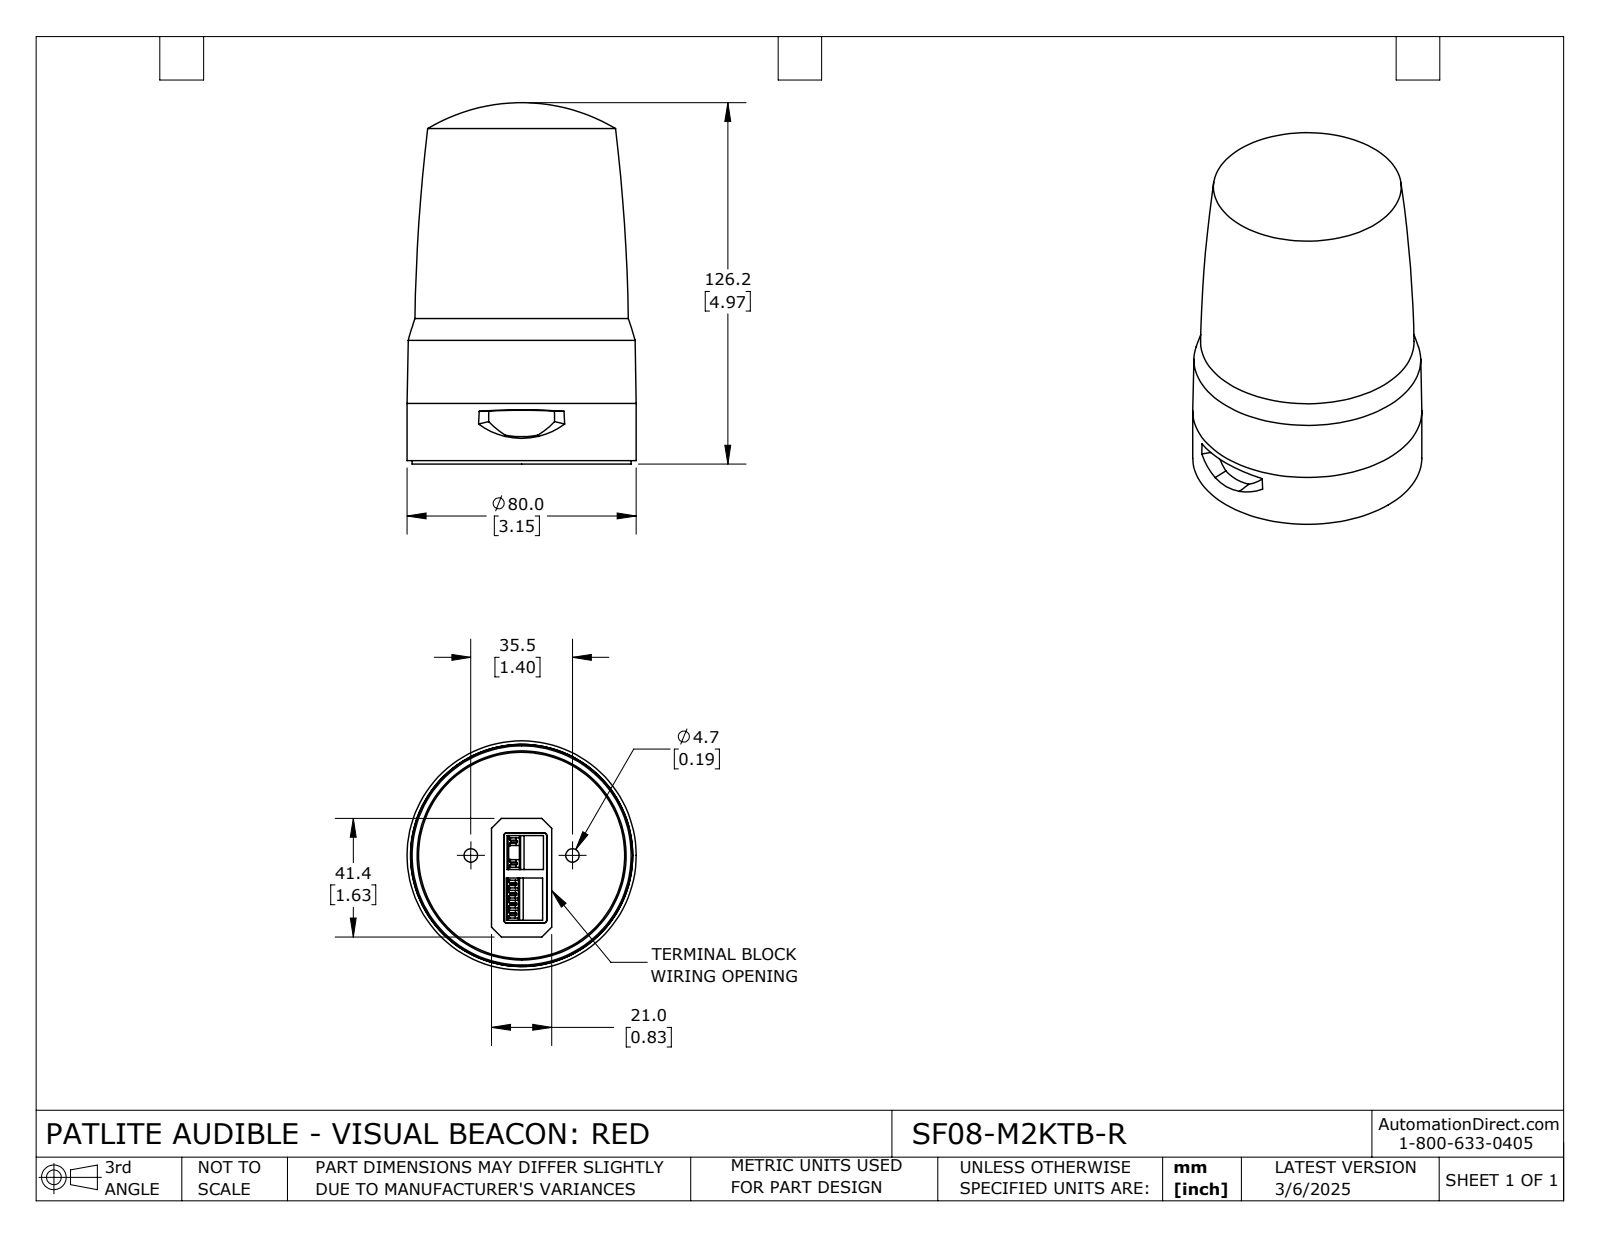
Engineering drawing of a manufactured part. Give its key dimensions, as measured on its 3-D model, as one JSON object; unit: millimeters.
{"part_name": "SF08-M2KTB-R", "step_written_by": "SolidWorks 2024 (CONFIG_CONTROL_DESIGN)", "units": "millimeters", "bodies": {"solids": 2, "faces": 262, "planar": 168, "cylindrical": 32, "other": 62}, "overall_size": [126.2, 80, 80], "volume_mm3": 488153, "surface_area_mm2": 54584, "round_holes": [[4.7, 2], [12.2, 2], [73, 1]], "round_bosses_or_shafts": [[80, 1], [76.5, 1], [74.6, 1], [72, 1]], "partial_cylinders_radius": [[1, 4], [0.3, 2], [34.6, 1], [35, 1]], "face_to_face_distances": [15.7, 6.3, 9.4, 3, 5.1, 14.5, 3.15, 6.15, 1.3, 12.45], "hole_center_spacings": [17.75, 35.5]}
